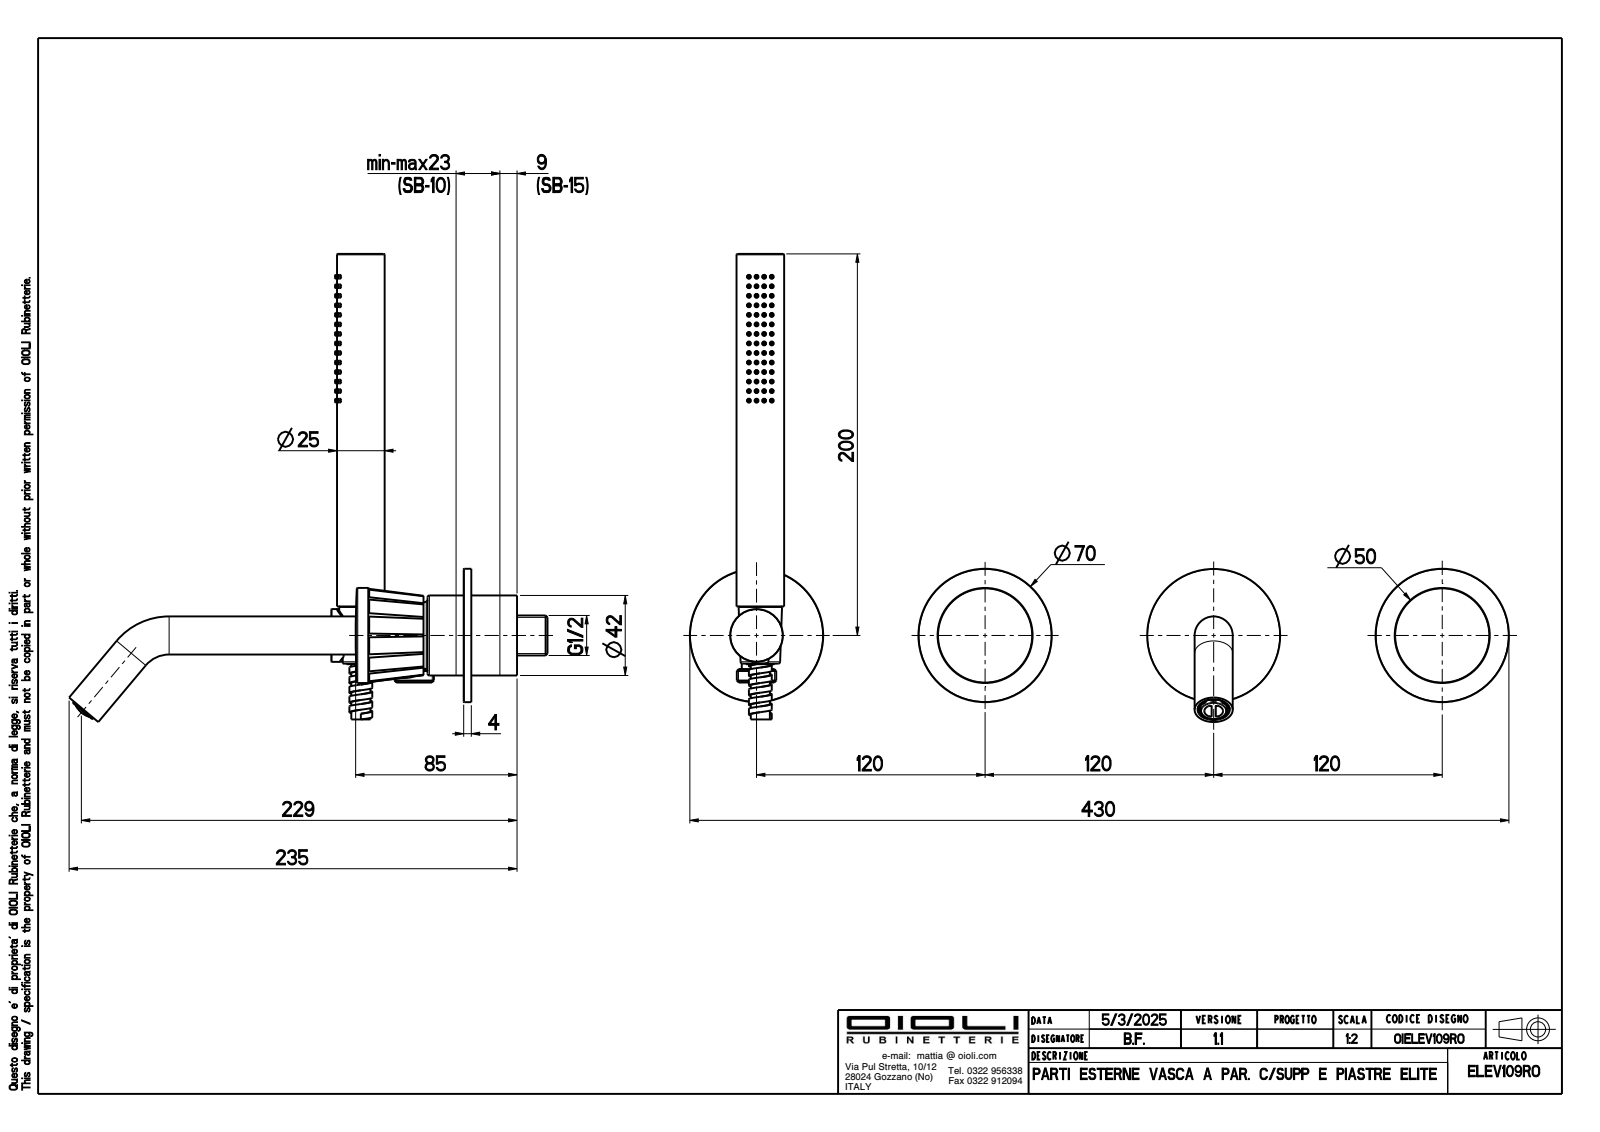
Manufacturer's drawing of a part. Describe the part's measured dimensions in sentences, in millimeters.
The part is named "OIBR00949; OIBR00242; OIBR00948; OIAQ00013 (+8 more)". Its 3-D file was written by "CREO PARAMETRIC BY PTC INC, 2024493 (CONFIG_CONTROL_DESIGN)". It is 22 solids with 1669 faces: 705 planar, 412 cylindrical and 552 other. Overall it measures 529.08 by 465.81 by 320.89 millimeters. Its volume is 269 897 cubic millimeters and its surface area 158 766 square millimeters. Round holes: 4 of diameter 4.2, 3 of diameter 15.5, 2 of diameter 4, 2 of diameter 5.3, 2 of diameter 6.5, 2 of diameter 9.5, 2 of diameter 14, 2 of diameter 14.5, 2 of diameter 15, 2 of diameter 17, 2 of diameter 30, 2 of diameter 39.5. Round bosses or shafts: 5 of diameter 5, 4 of diameter 16.5, 3 of diameter 70, 2 of diameter 49.9, 2 of diameter 42, 2 of diameter 20, 2 of diameter 18, 1 of diameter 69.8. Partial cylindrical surfaces (rounded edges, fillets, slot ends): 24 of radius 0.1, 8 of radius 0.9, 5 of radius 0.6, 4 of radius 5, 4 of radius 6.8, 3 of radius 0.45, 2 of radius 10, 1 of radius 2.5. The main face-to-face distances are 7.65, 4, 40.15, 2, 3.5, 36.65, 42.15, 38.65, 33, 40.65. The hole center spacings are 13.06, 17.8, 28.07, 45.84, 133.02, 134.85, 142.56, 182.2.
